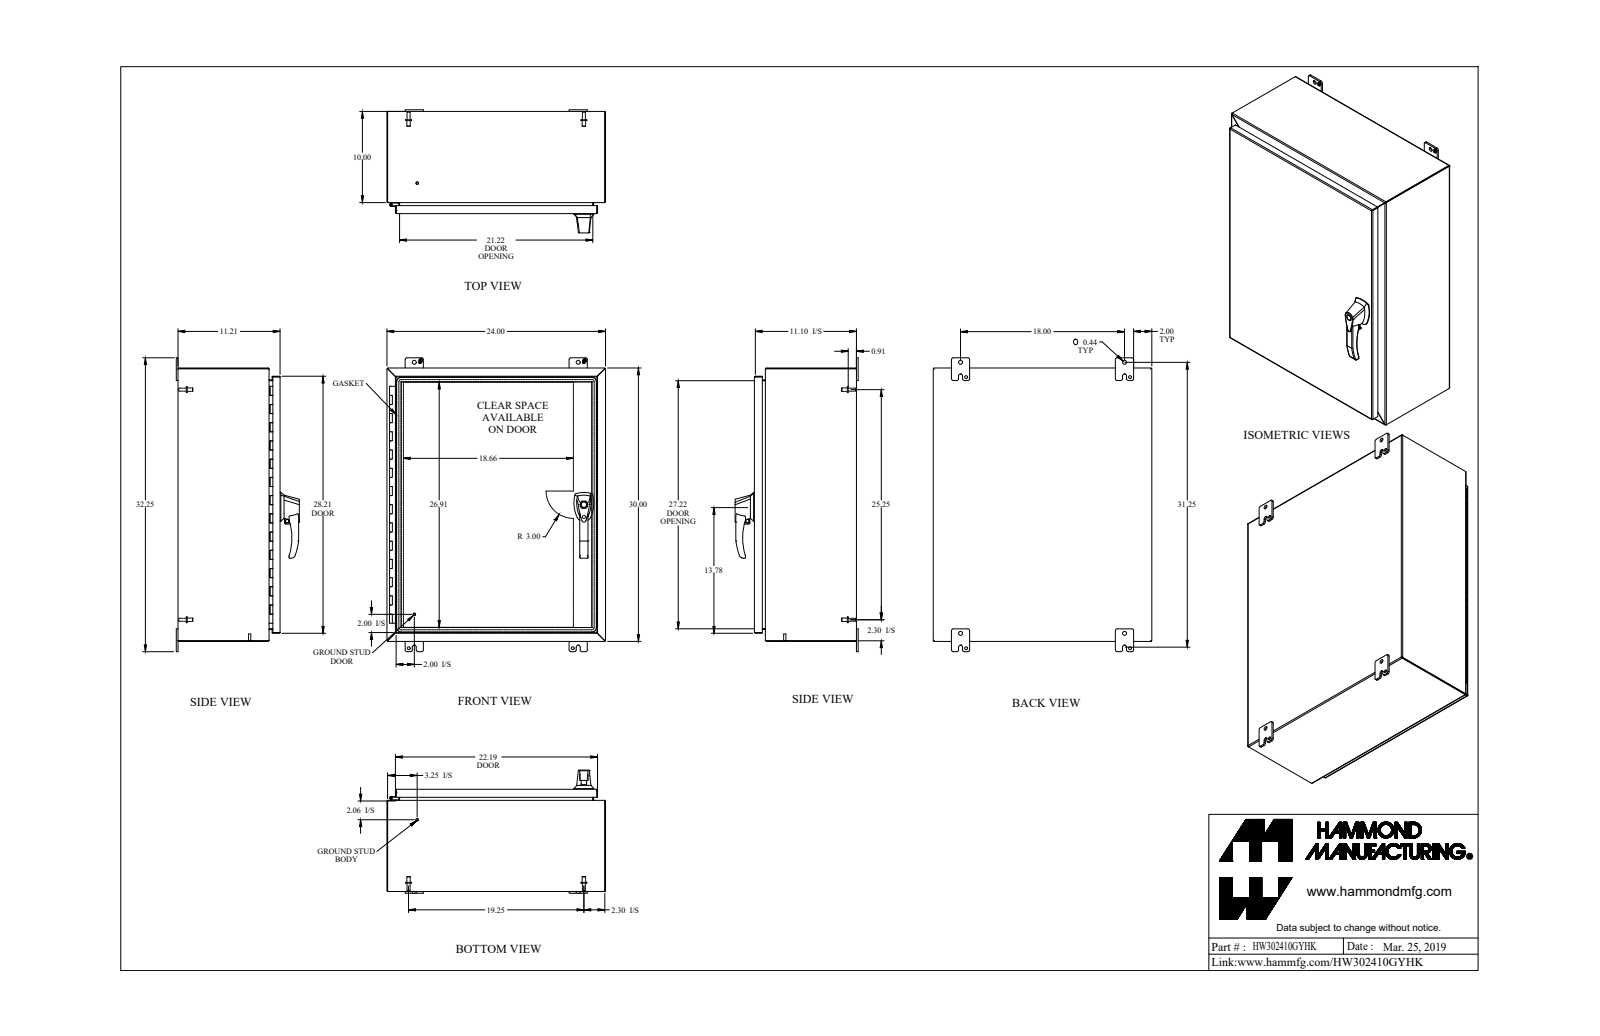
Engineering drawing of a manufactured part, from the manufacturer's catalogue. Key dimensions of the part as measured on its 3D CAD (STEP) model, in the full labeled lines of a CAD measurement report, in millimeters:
Part name (STEP PRODUCT): HW302410GYHK
STEP written by: SolidWorks 2018 (AUTOMOTIVE_DESIGN)
Units: millimetres
Bodies: 39 solids, 1429 faces (696 planar, 589 cylindrical, 144 other)
Overall size (bounding box): 819.2 × 609.6 × 343.2
Volume: 3 882 000 mm³ · Surface area: 3 956 000 mm²
Round holes (diameter × count): ⌀4.5 ×6, ⌀8 ×6, ⌀11.1 ×4, ⌀6.4 ×3, ⌀6.7 ×3, ⌀10.5 ×3, ⌀5 ×2, ⌀6.5 ×2, ⌀10 ×2, ⌀4.7 ×1, ⌀5.9 ×1, ⌀8.5 ×1
Round bosses / shafts (diameter × count): ⌀9.5 ×9, ⌀6.4 ×7, ⌀4 ×6, ⌀16.5 ×4, ⌀8.4 ×4, ⌀25.4 ×3, ⌀16 ×2, ⌀13 ×2
Partial cylindrical surfaces — rounded edges, fillets, slot ends (radius × count): R6.4 ×27, R4.8 ×24, R0.9 ×20, R2.7 ×20, R1.5 ×12, R3.2 ×9, R1.1 ×8, R5.5 ×8
Main face-to-face distances: 1.8, 1.8, 282.9, 281.1, 284.7, 282.9, 607.8, 760.2, 605.9, 609.6
Hole centre spacings: 44.1, 457.2, 755.7, 883.2, 282.4, 282.4, 564.8, 28.2
